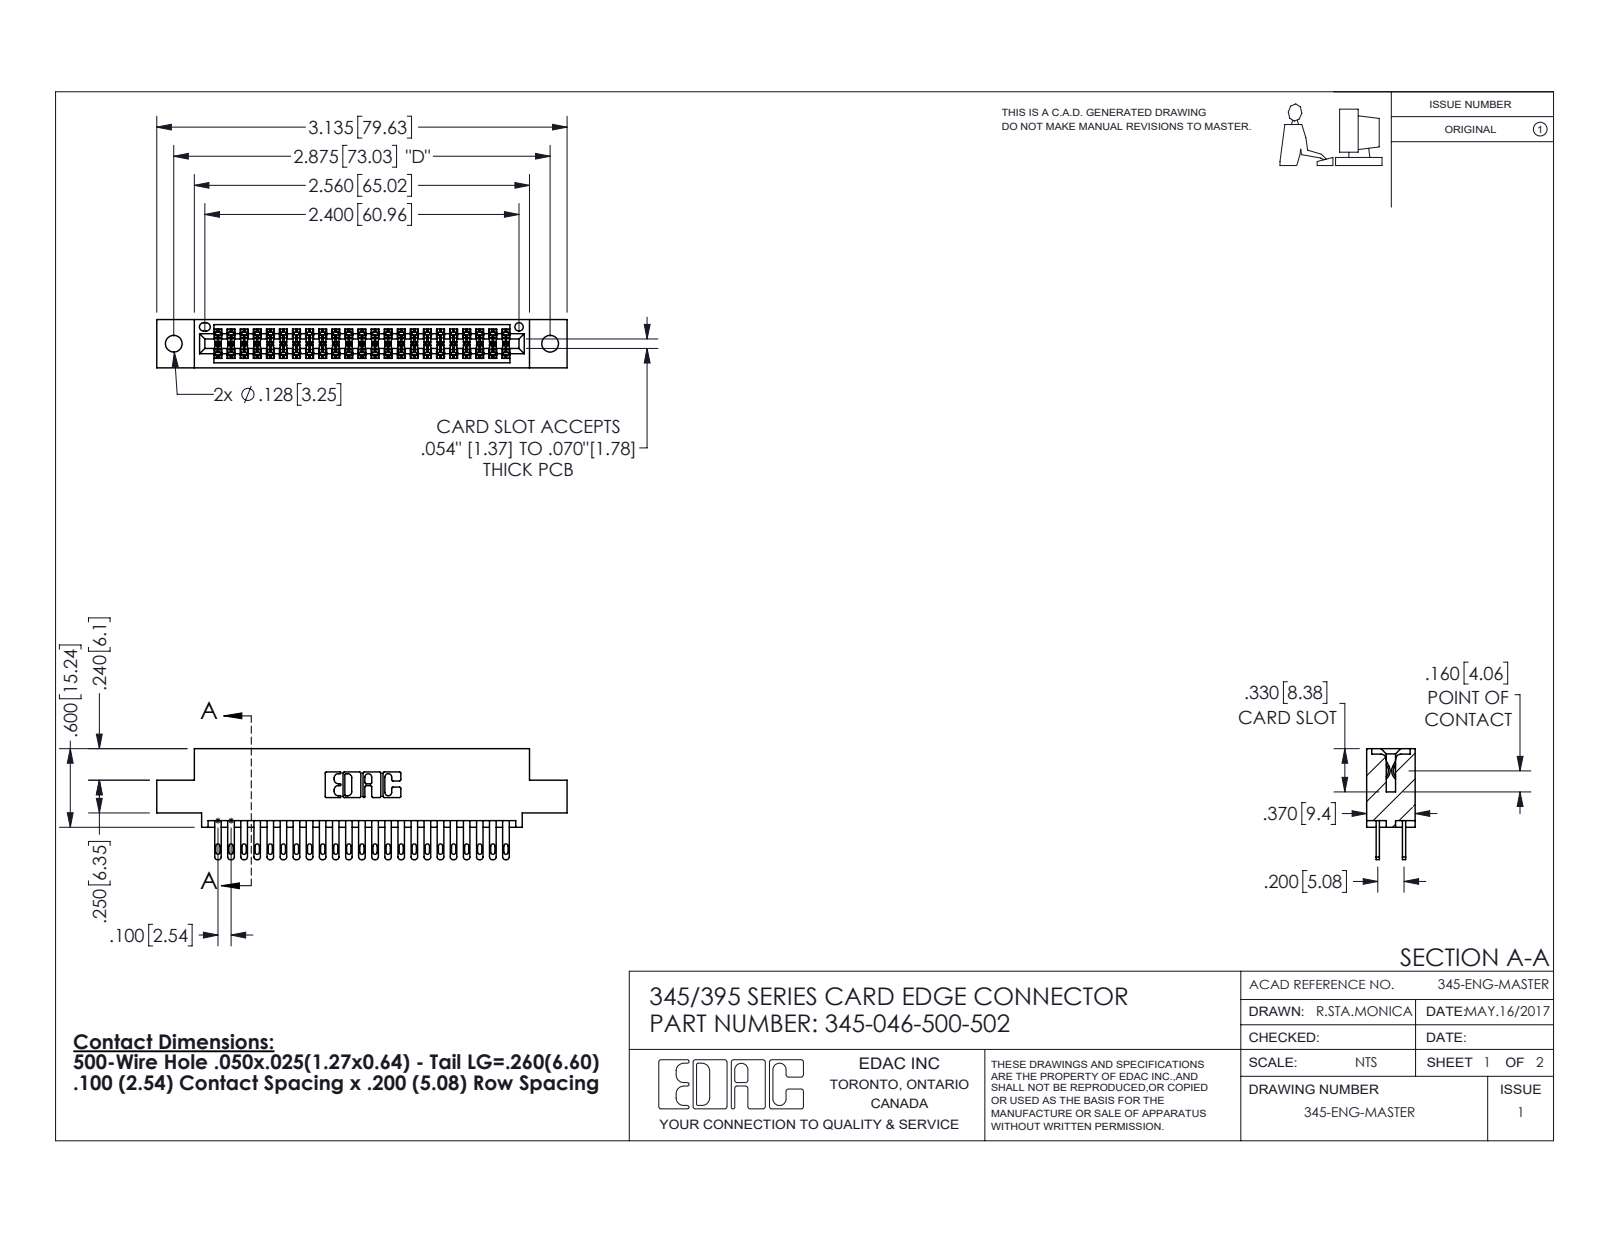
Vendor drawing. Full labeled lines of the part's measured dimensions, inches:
Part name (STEP PRODUCT): 345-046-500-502; 345-292-001_345-293-100; 345 Part_0.110 Offset - 0.128 Dia
STEP written by: SolidWorks 2016 (CONFIG_CONTROL_DESIGN)
Units: inches
Bodies: 47 solids, 2246 faces (1326 planar, 920 cylindrical, 0 other)
Overall size (bounding box): 3.135 × 0.847 × 0.37
Volume: 0.463 in³ · Surface area: 17.27 in²
Round holes (diameter × count): ⌀0.128 ×2, ⌀0.064 ×1
Partial cylindrical surfaces — rounded edges, fillets, slot ends (radius × count): R0.006 ×69, R0.016 ×46, R0.02 ×46, R0.01 ×22, R0.007 ×6, R0.031 ×6, R0.026 ×3, R0.014 ×2
Main face-to-face distances: 0.072, 0.298, 0.2, 0.098, 0.272, 0.025, 0.37, 0.225, 0.175, 0.149
Hole centre spacings: 0.27, 2.641, 2.875
